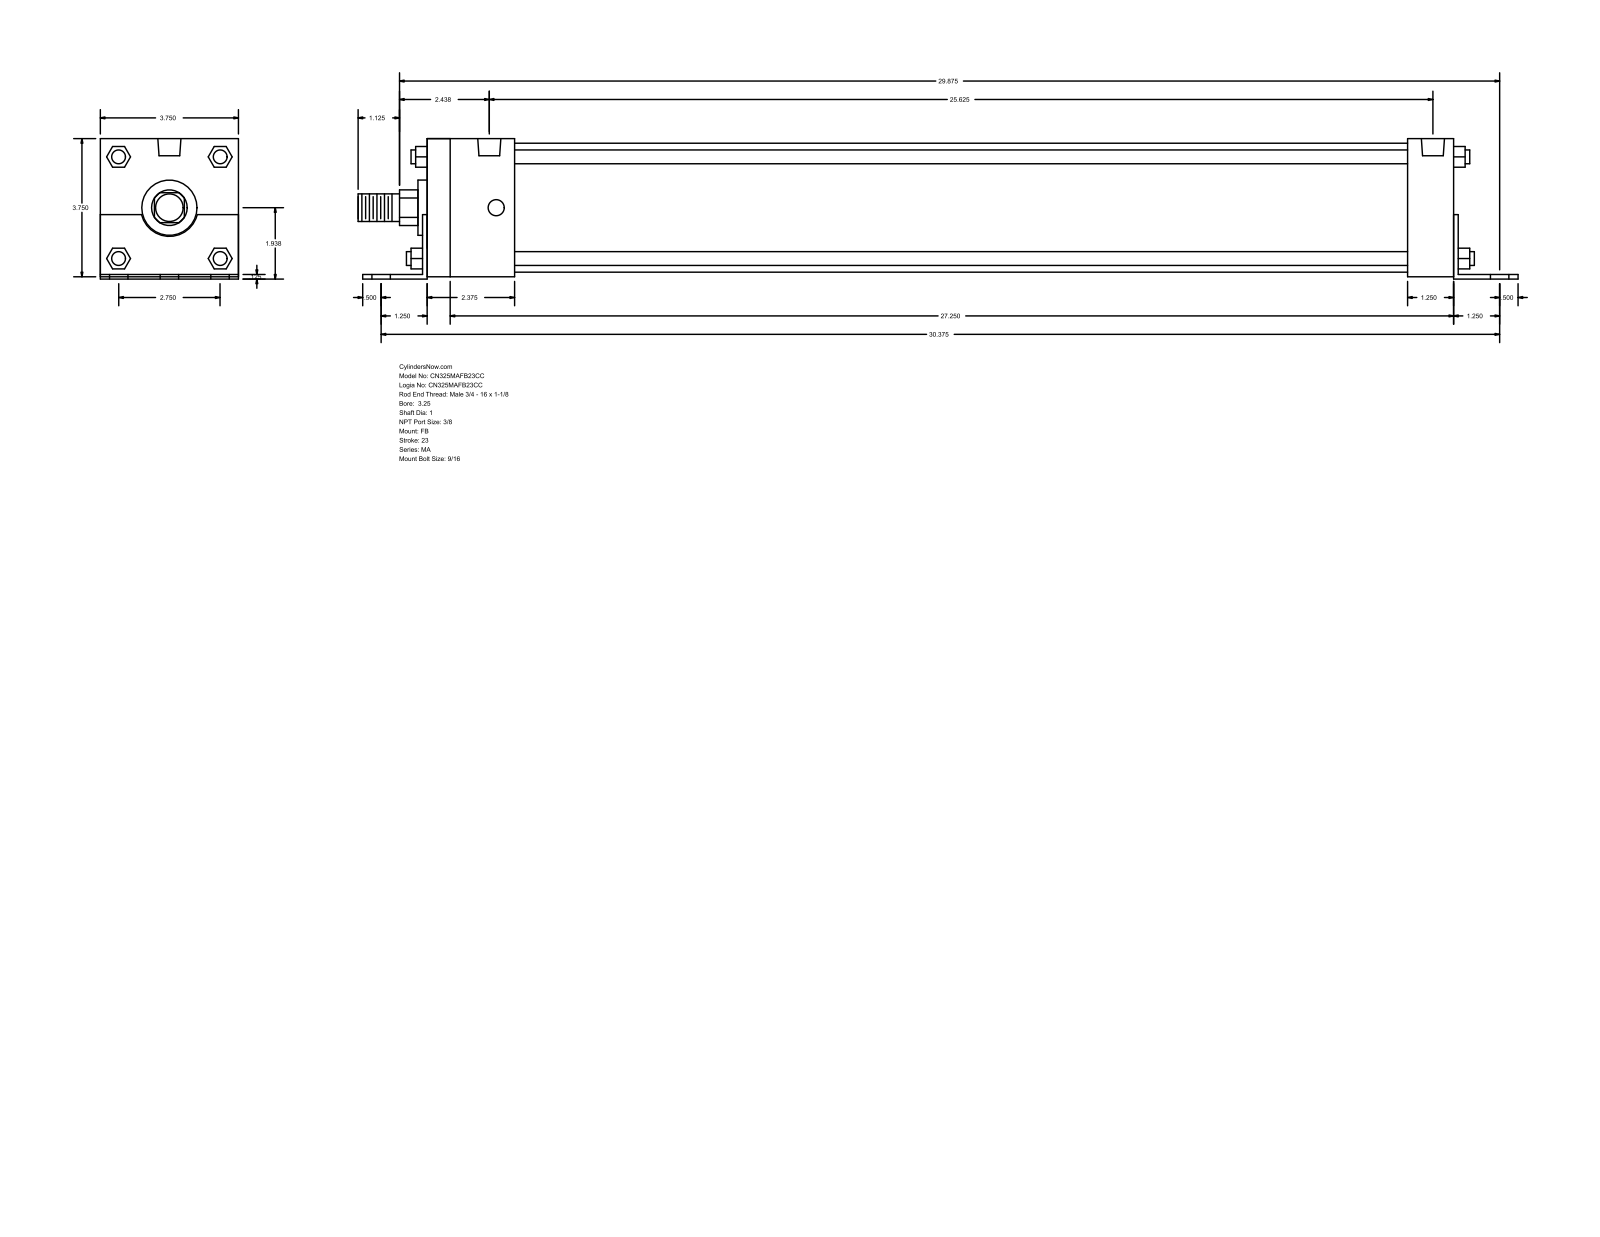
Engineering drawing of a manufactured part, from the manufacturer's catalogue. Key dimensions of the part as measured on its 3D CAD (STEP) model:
Part name (STEP PRODUCT): MA_FB__0325_1
STEP written by: GSSL Pune (CONFIG_CONTROL_DESIGN)
Units: millimetres
Bodies: 0 solids, 140 faces (105 planar, 35 cylindrical, 0 other)
Overall size (bounding box): 800.1 × 96.84 × 95.25
Round holes (diameter × count): ⌀14.29 ×6, ⌀11.11 ×4, ⌀15.93 ×2
Round bosses / shafts (diameter × count): ⌀9.53 ×4, ⌀88.9 ×1, ⌀38.1 ×1, ⌀25.4 ×1, ⌀19.05 ×1
Partial cylindrical surfaces — rounded edges, fillets, slot ends (radius × count): R12.29 ×1, R19.81 ×1
Main face-to-face distances: 95.24, 3.17, 1.59, 96.83, 1.58, 93.66, 711.2, 708.03, 714.37, 679.45
Hole centre spacings: 34.92, 772.32, 771.53, 57.78, 61.65, 69.84, 82.38, 86.71
